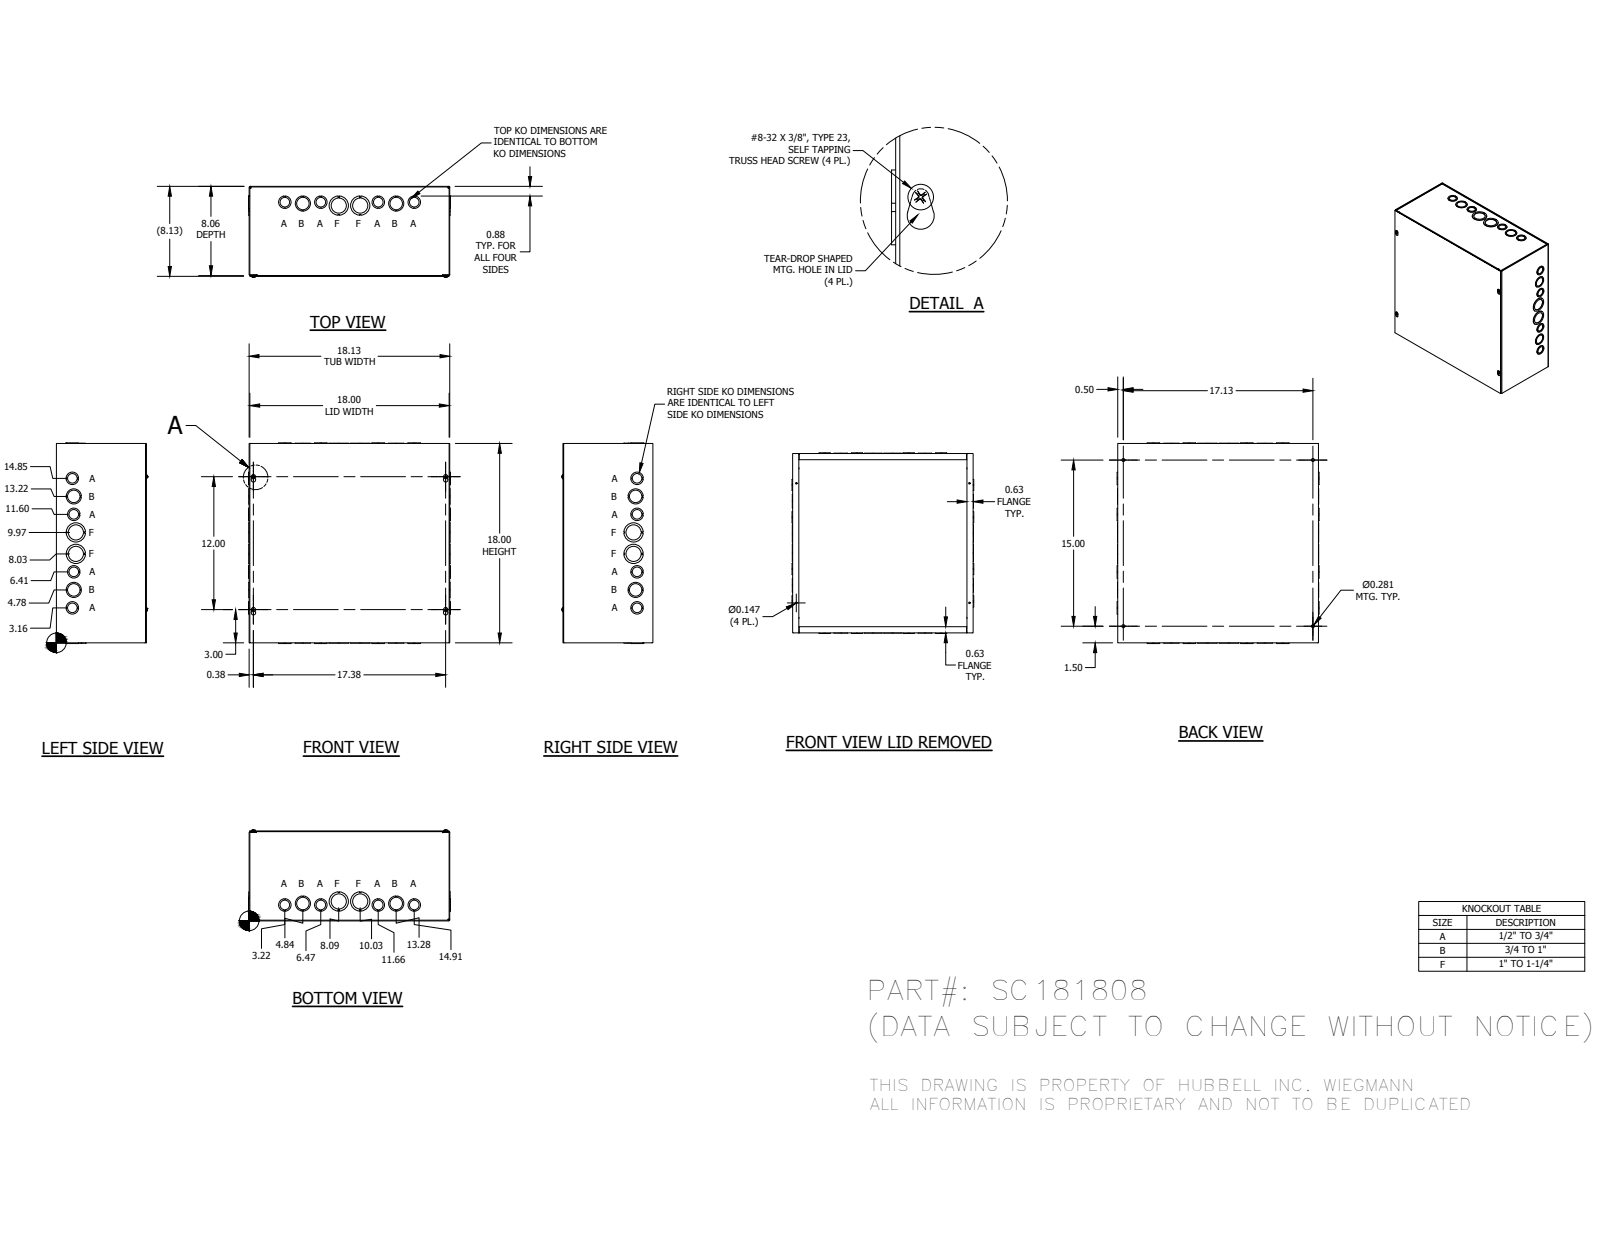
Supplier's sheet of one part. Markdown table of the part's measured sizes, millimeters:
| quantity | value |
| --- | --- |
| part name | SC181808BLR; SC1808TB; SC1818LPA; 34056 (+1 more) |
| STEP written by | Autodesk Inventor 2014 (AUTOMOTIVE_DESIGN) |
| units | millimeters |
| bodies | 37 solids, 1167 faces (859 planar, 240 cylindrical, 68 other) |
| overall size | 463.55 × 460.38 × 208.92 |
| round holes (diameter × count) | 28.57 × 14, 22.22 × 10, 34.92 × 8, 3.73 × 4, 7.14 × 4, 44.45 × 4 |
| round bosses / shafts (diameter × count) | 9.75 × 4, 4.17 × 4 |
| partial cylindrical surfaces (radius × count) | 0.79 × 12, 2.38 × 12, 3.17 × 4, 5.16 × 4 |
| main face-to-face distances | 1.59, 204.79, 203.2, 206.38, 457.2, 455.61, 458.79, 460.38, 454.02, 3.18 |
| hole center spacings | 38.23, 41.39, 41.4, 42.03, 82.55, 82.69, 90.9, 124.07 |
